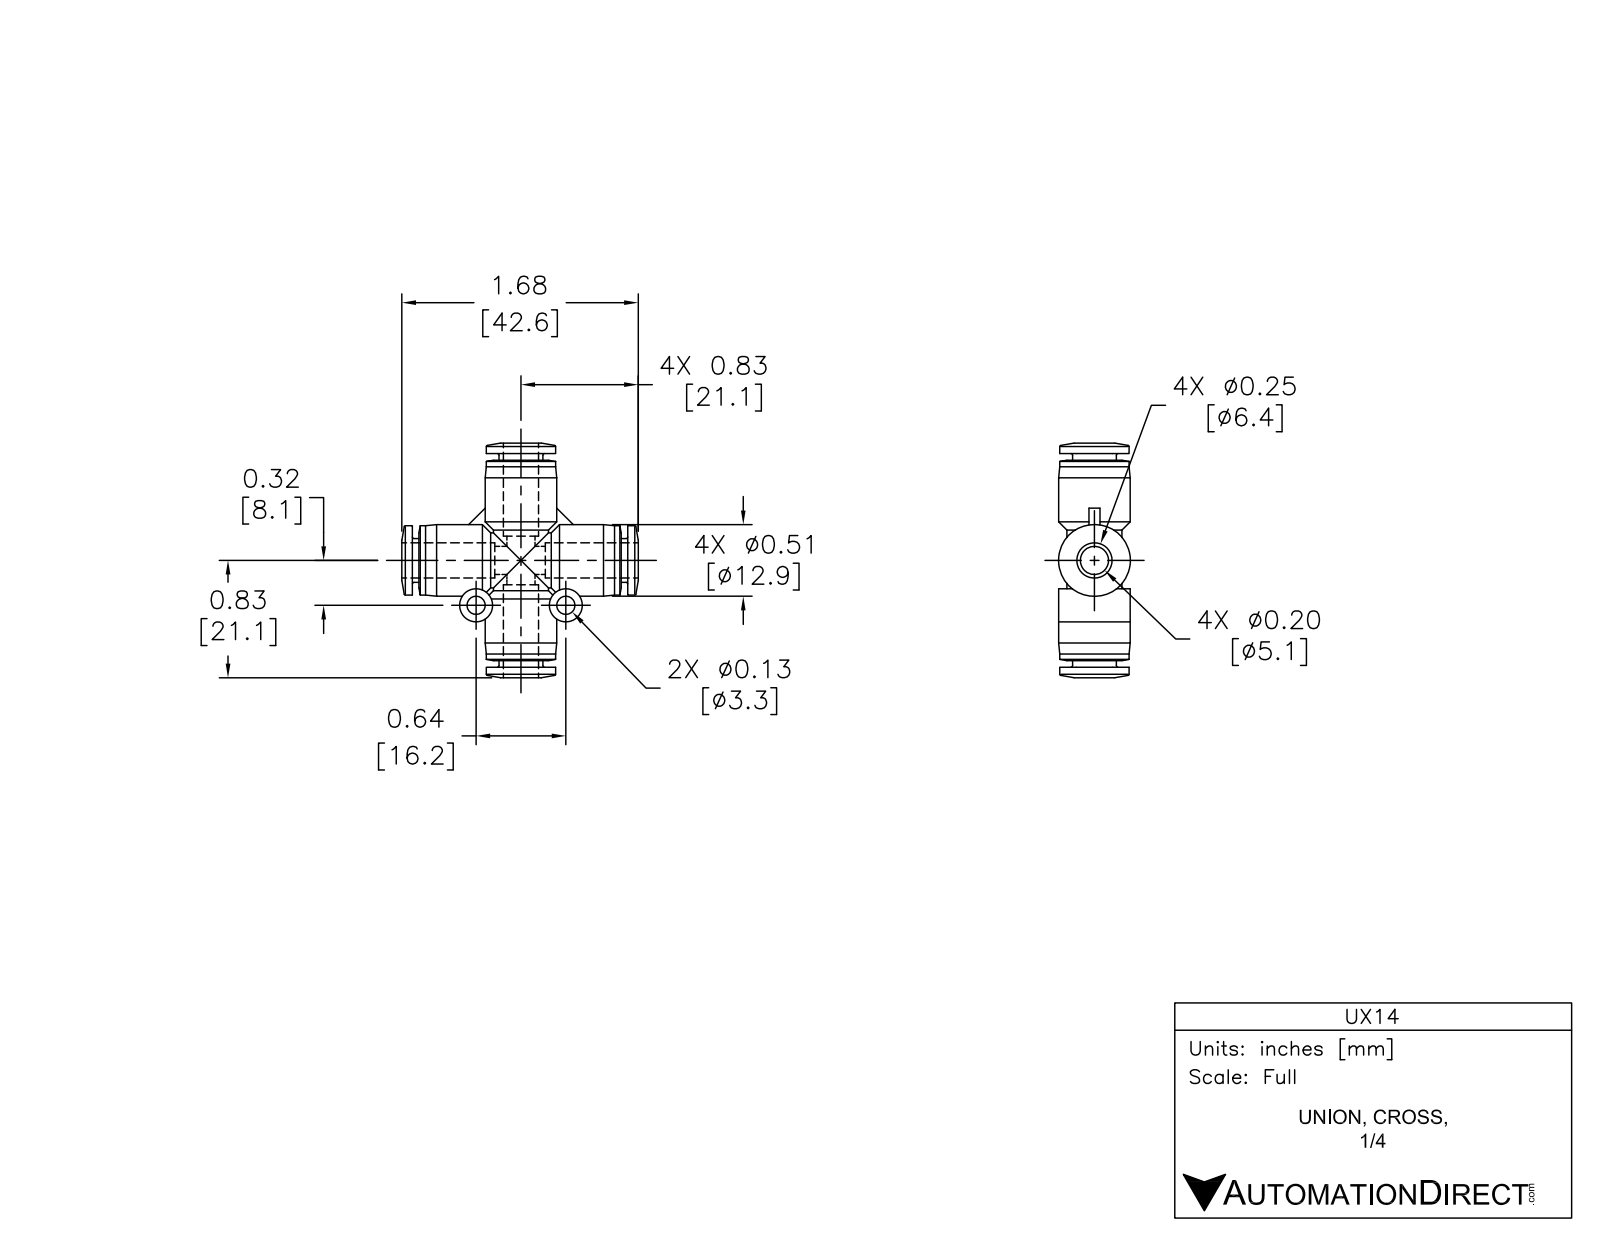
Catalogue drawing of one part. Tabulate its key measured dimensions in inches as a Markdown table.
| quantity | value |
| --- | --- |
| part name | UX14 |
| STEP written by | SolidWorks 2015 (AUTOMOTIVE_DESIGN) |
| units | inches |
| bodies | 1 solid, 157 faces (26 planar, 65 cylindrical, 66 other) |
| overall size | 1.677 × 1.677 × 0.512 |
| volume | 0.401 in³ |
| surface area | 9.082 in² |
| round holes (diameter × count) | 0.13 × 2, 0.197 × 2, 0.258 × 2 |
| round bosses / shafts (diameter × count) | 0.512 × 2, 0.496 × 2, 0.394 × 2, 0.313 × 2, 0.236 × 2 |
| main face-to-face distances | 1.528, 1.48, 0.047, 1.433, 0.587, 0.941, 0.539, 0.894, 0.512, 0.217 |
| hole center spacings | 0.642 |
